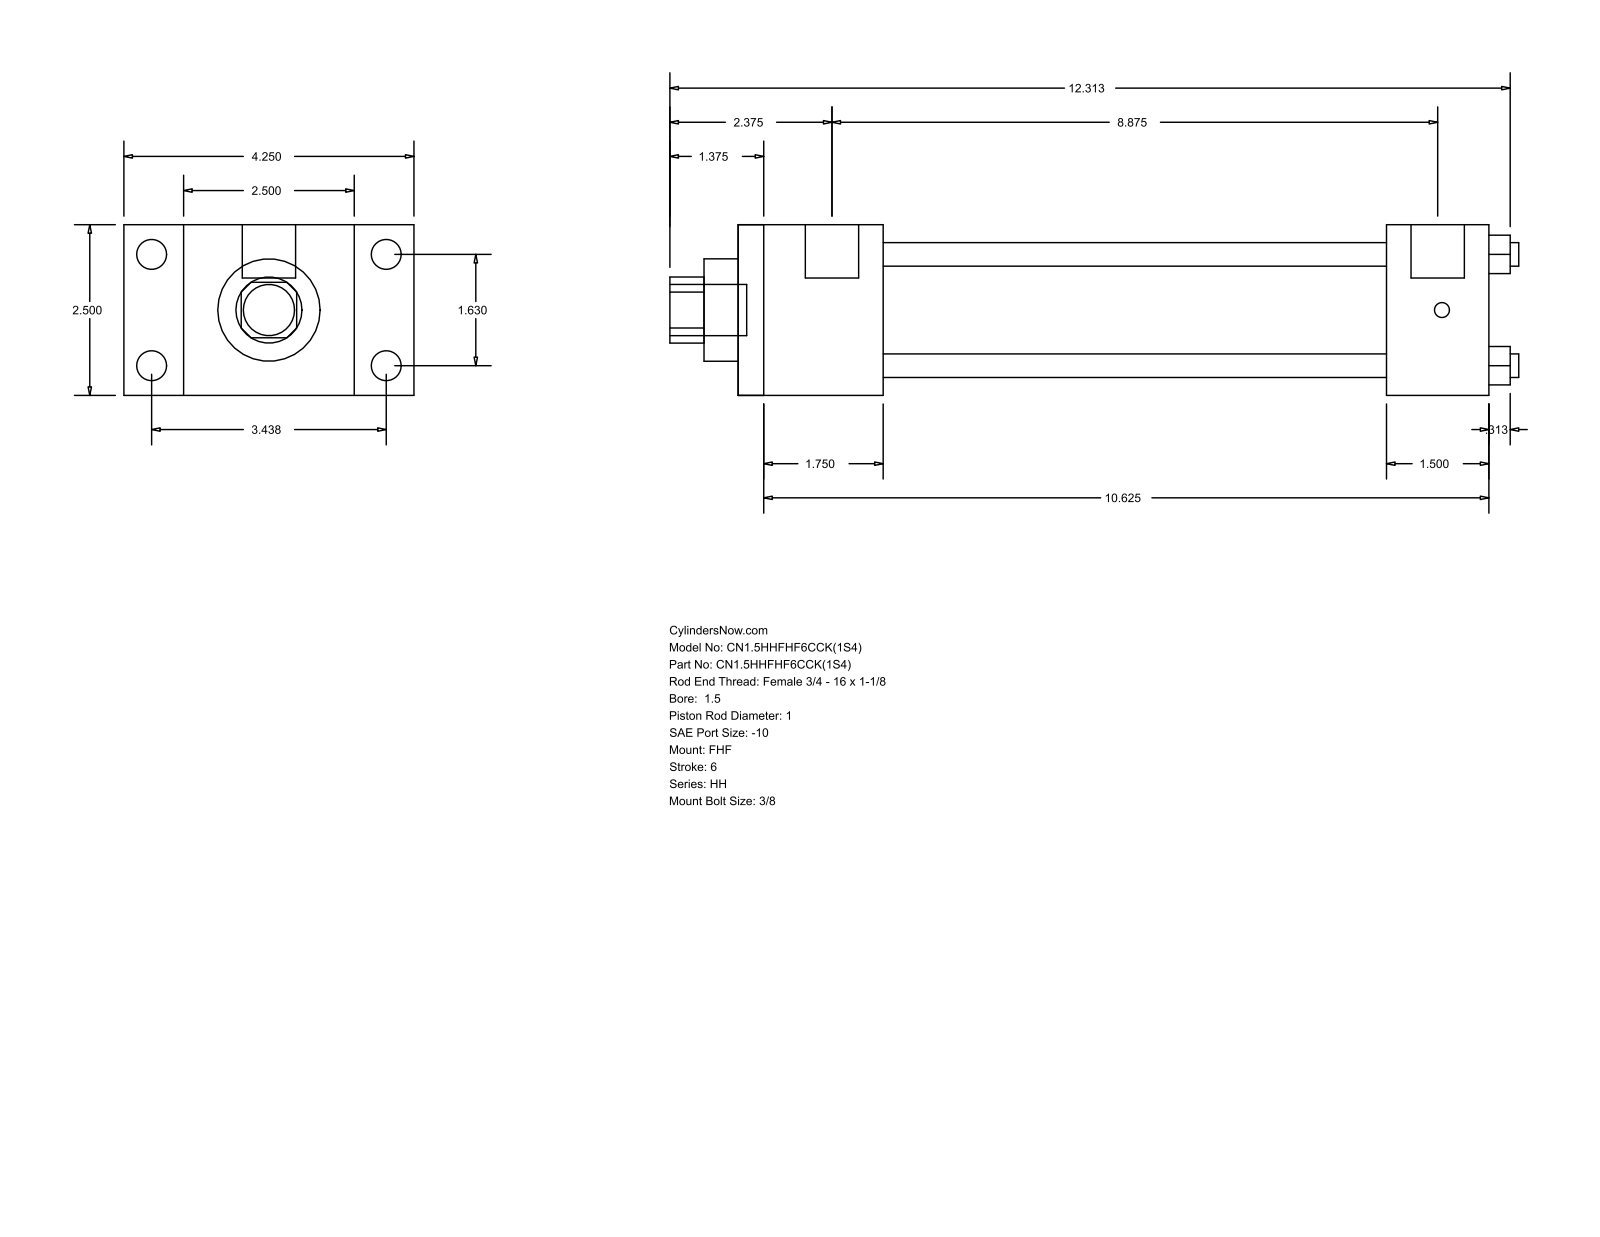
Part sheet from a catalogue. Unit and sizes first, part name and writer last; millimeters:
Units: millimetres
Overall size (bounding box): 315.91 × 107.95 × 63.5
Round holes (diameter × count): ⌀8.76 ×4, ⌀25.4 ×1, ⌀38.1 ×1, ⌀44.45 ×1
Round bosses / shafts (diameter × count): ⌀11.13 ×4, ⌀5.56 ×4, ⌀19.84 ×2, ⌀19.05 ×1
Partial cylindrical surfaces — rounded edges, fillets, slot ends (radius × count): R12.29 ×1
Main face-to-face distances: 63.5, 22.23, 85.73, 53.98, 107.96, 279.4, 225.42, 241.3, 187.32, 38.1
Hole centre spacings: 29.27, 41.4, 58.55
Bodies: 0 solids, 88 faces (60 planar, 28 cylindrical, 0 other)
Part name (STEP PRODUCT): HH_FHF__0150_1
STEP written by: GSSL Pune (CONFIG_CONTROL_DESIGN)
